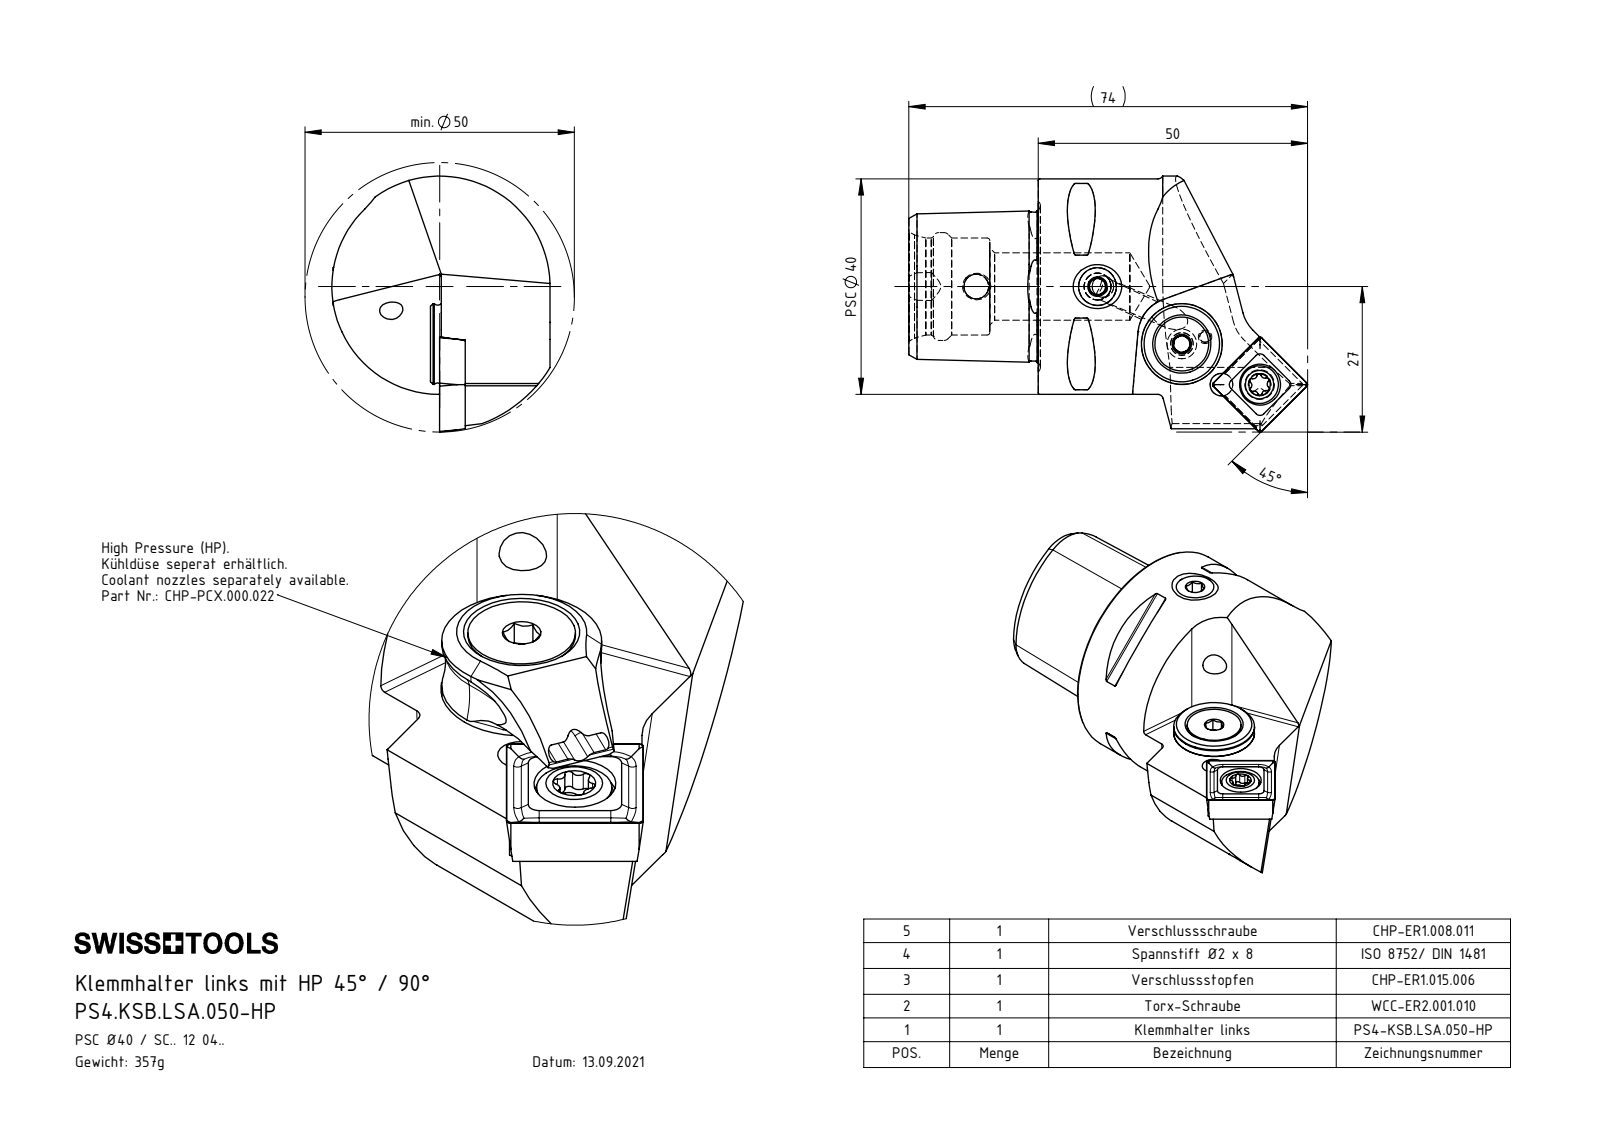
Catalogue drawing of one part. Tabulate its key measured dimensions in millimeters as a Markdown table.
| quantity | value |
| --- | --- |
| part name | DIN 7991 - M5x15; CHP-ER1.015.006_A; SCMT120404; WCC-ER2.001.010_A (+6 more) |
| STEP written by | SolidWorks 2022 (CONFIG_CONTROL_DESIGN) |
| units | millimeters |
| bodies | 8 solids, 380 faces (88 planar, 100 cylindrical, 192 other) |
| overall size | 74 × 47.5 × 40.5 |
| volume | 53 979 mm³ |
| surface area | 16 081 mm² |
| round holes (diameter × count) | 4.2 × 5, 1.2 × 1, 2 × 1, 2.5 × 1, 3 × 1, 4 × 1, 4.6 × 1, 5 × 1, 5.2 × 1, 5.5 × 1, 7 × 1, 7.6 × 1 |
| round bosses / shafts (diameter × count) | 5 × 2, 40 × 1, 15 × 1, 13.4 × 1, 10 × 1, 8 × 1, 7 × 1, 5.5 × 1 |
| partial cylindrical surfaces (radius × count) | 0.3 × 8, 0.39 × 6, 0.69 × 6, 0.5 × 2, 3 × 1, 7 × 1, 20.5 × 1, 25 × 1 |
| main face-to-face distances | 20.2, 15.7, 4.5, 15.74, 4.46, 24, 15.52, 35.3, 15, 22.1 |
| hole center spacings | 2.52, 4.5, 5.57, 7.06, 8.09, 9.97, 12.37, 14.83 |
